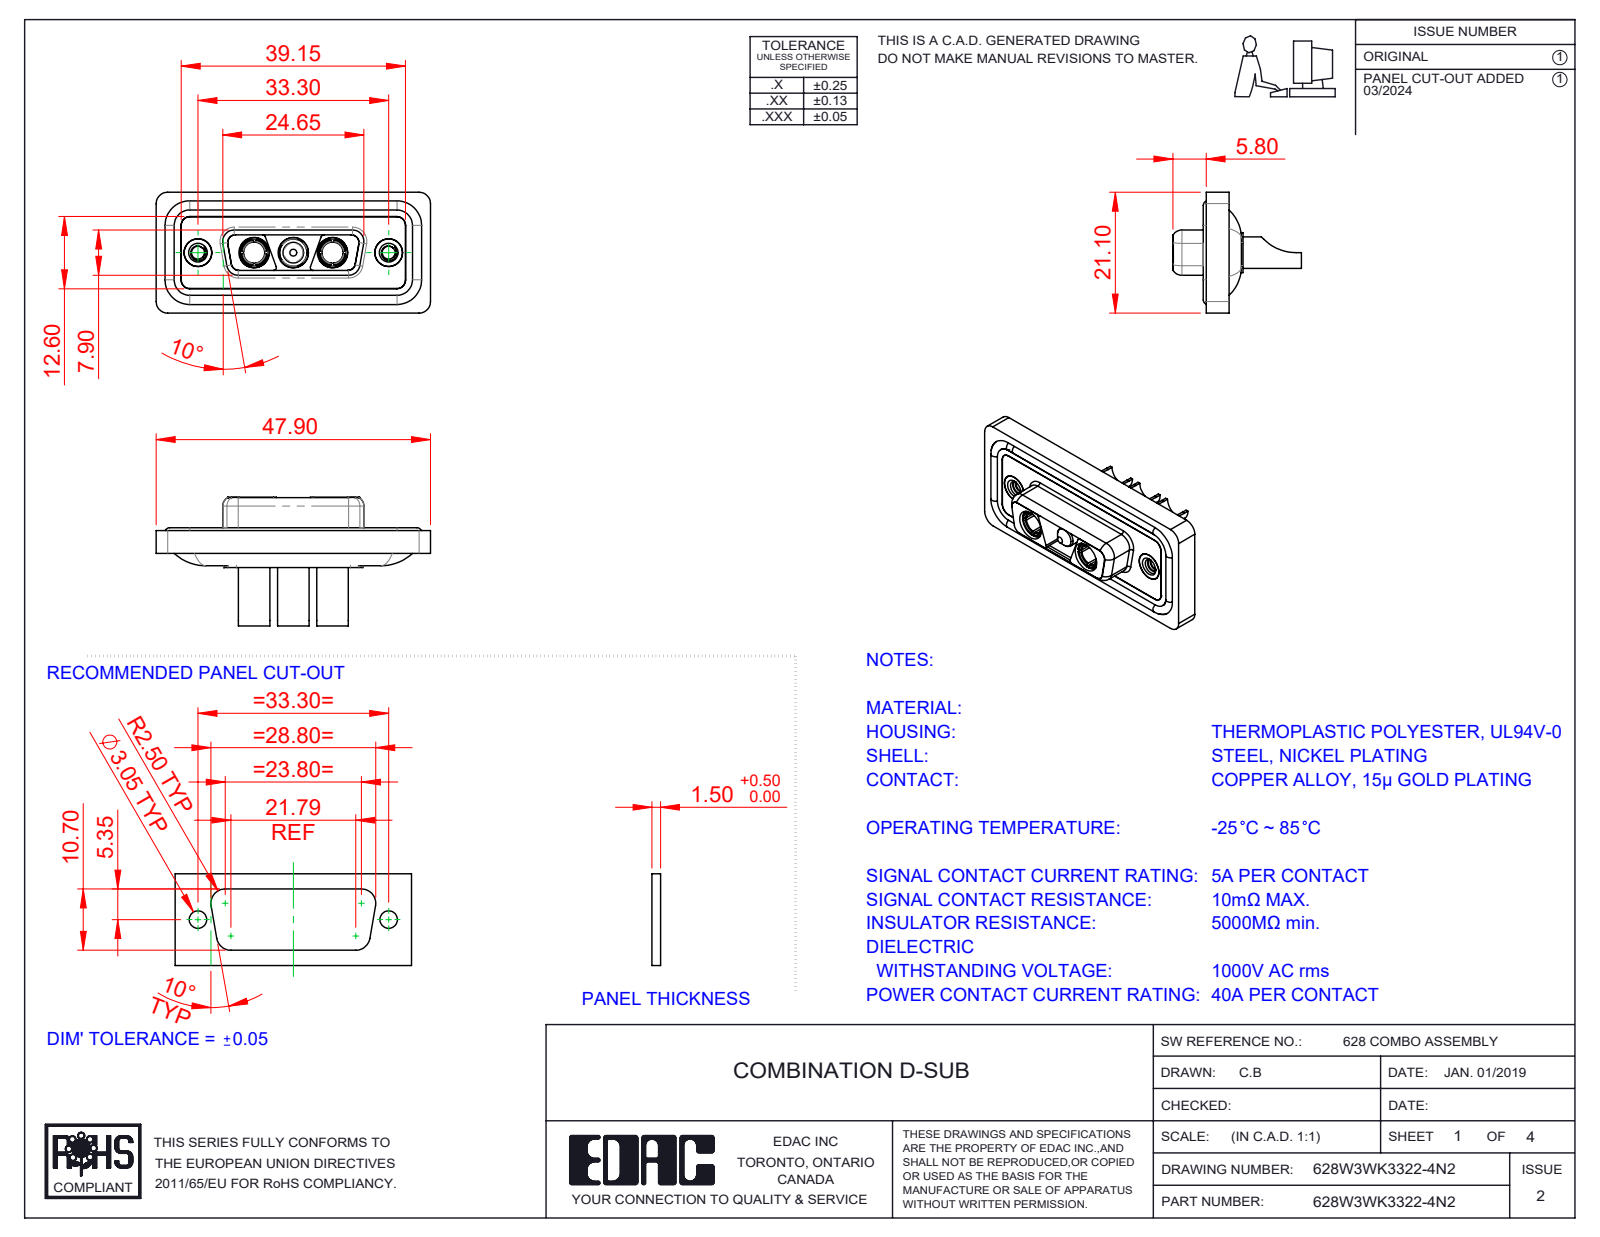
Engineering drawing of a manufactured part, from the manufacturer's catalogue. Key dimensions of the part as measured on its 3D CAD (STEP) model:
Part name (STEP PRODUCT): 628W3WK3322-4N2; Power Socket_40A SC; 628Combo Housing_3WK3; 628Combo Waterproof Housing_15 Contacts (+4 more)
STEP written by: SolidWorks 2023 (CONFIG_CONTROL_DESIGN)
Units: millimetres
Bodies: 13 solids, 593 faces (184 planar, 261 cylindrical, 148 other)
Overall size (bounding box): 47.9 × 22.45 × 21.1
Volume: 5 998 mm³ · Surface area: 9 924 mm²
Round holes (diameter × count): ⌀4.85 ×5, ⌀4.6 ×3, ⌀5.3 ×3, ⌀2.26 ×2, ⌀3.7 ×2, ⌀4 ×2, ⌀4.05 ×2, ⌀5 ×2
Round bosses / shafts (diameter × count): ⌀1.6 ×4, ⌀5.5 ×3, ⌀5.2 ×3, ⌀4.75 ×3, ⌀3.75 ×3, ⌀4.96 ×2, ⌀4.95 ×2, ⌀4.8 ×2
Partial cylindrical surfaces — rounded edges, fillets, slot ends (radius × count): R1.5 ×22, R2 ×20, R1.35 ×12, R0.5 ×8, R1.6 ×8, R0.25 ×4, R0.6 ×4, R0.65 ×4
Main face-to-face distances: 0.4, 1.6, 0.5, 1.1, 2.9, 5.65, 1.8, 7.05, 5.35, 6.6
Hole centre spacings: 6.85, 9.8, 16.65, 23.5, 13.7, 33.3
